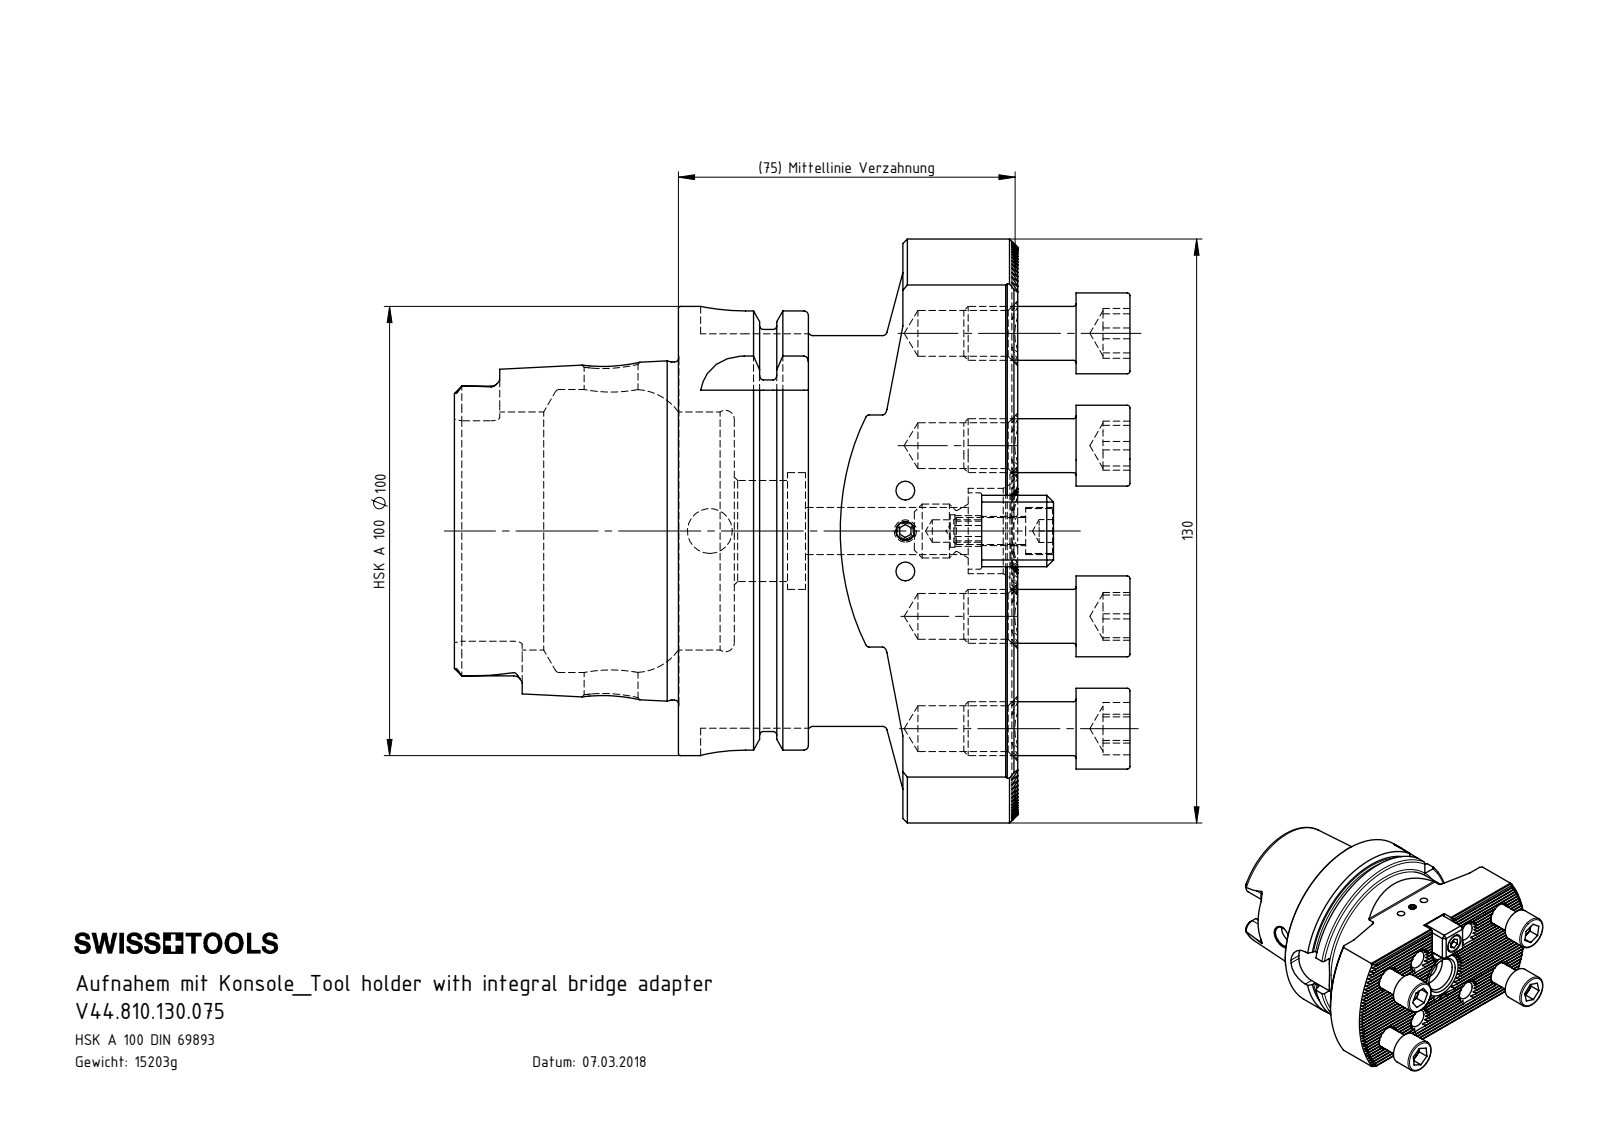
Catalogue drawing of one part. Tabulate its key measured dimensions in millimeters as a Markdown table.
| quantity | value |
| --- | --- |
| part name | Ko1-ER1.001.016_A; HA0.Ko1.K01.075; ISO 4762 - M6 x 16; ISO 4026 - M5 x 8 (+3 more) |
| STEP written by | SolidWorks 2017 (AUTOMOTIVE_DESIGN) |
| units | millimeters |
| bodies | 10 solids, 800 faces (513 planar, 175 cylindrical, 112 other) |
| overall size | 150.48 × 130 × 100 |
| volume | 592 882 mm³ |
| surface area | 96 768 mm² |
| round holes (diameter × count) | 10.2 × 8, 4.2 × 3, 10.5 × 2, 5 × 1, 6.5 × 1, 7.24 × 1, 10 × 1, 12 × 1, 19 × 1, 22.5 × 1, 26 × 1, 53 × 1 |
| round bosses / shafts (diameter × count) | 12 × 5, 18 × 4, 100 × 1, 91.95 × 1, 87 × 1, 75.26 × 1, 17 × 1, 10 × 1 |
| partial cylindrical surfaces (radius × count) | 0.14 × 34, 1.9 × 6, 4.88 × 4, 10 × 4, 0.8 × 2, 7.95 × 1, 65 × 1 |
| main face-to-face distances | 1.73, 17.32, 70, 8.66, 3.46, 5.2, 6.93, 15.59, 19.05, 3.47 |
| hole center spacings | 25, 27.59, 40, 47.17, 48.33, 63, 74.63, 9 |
